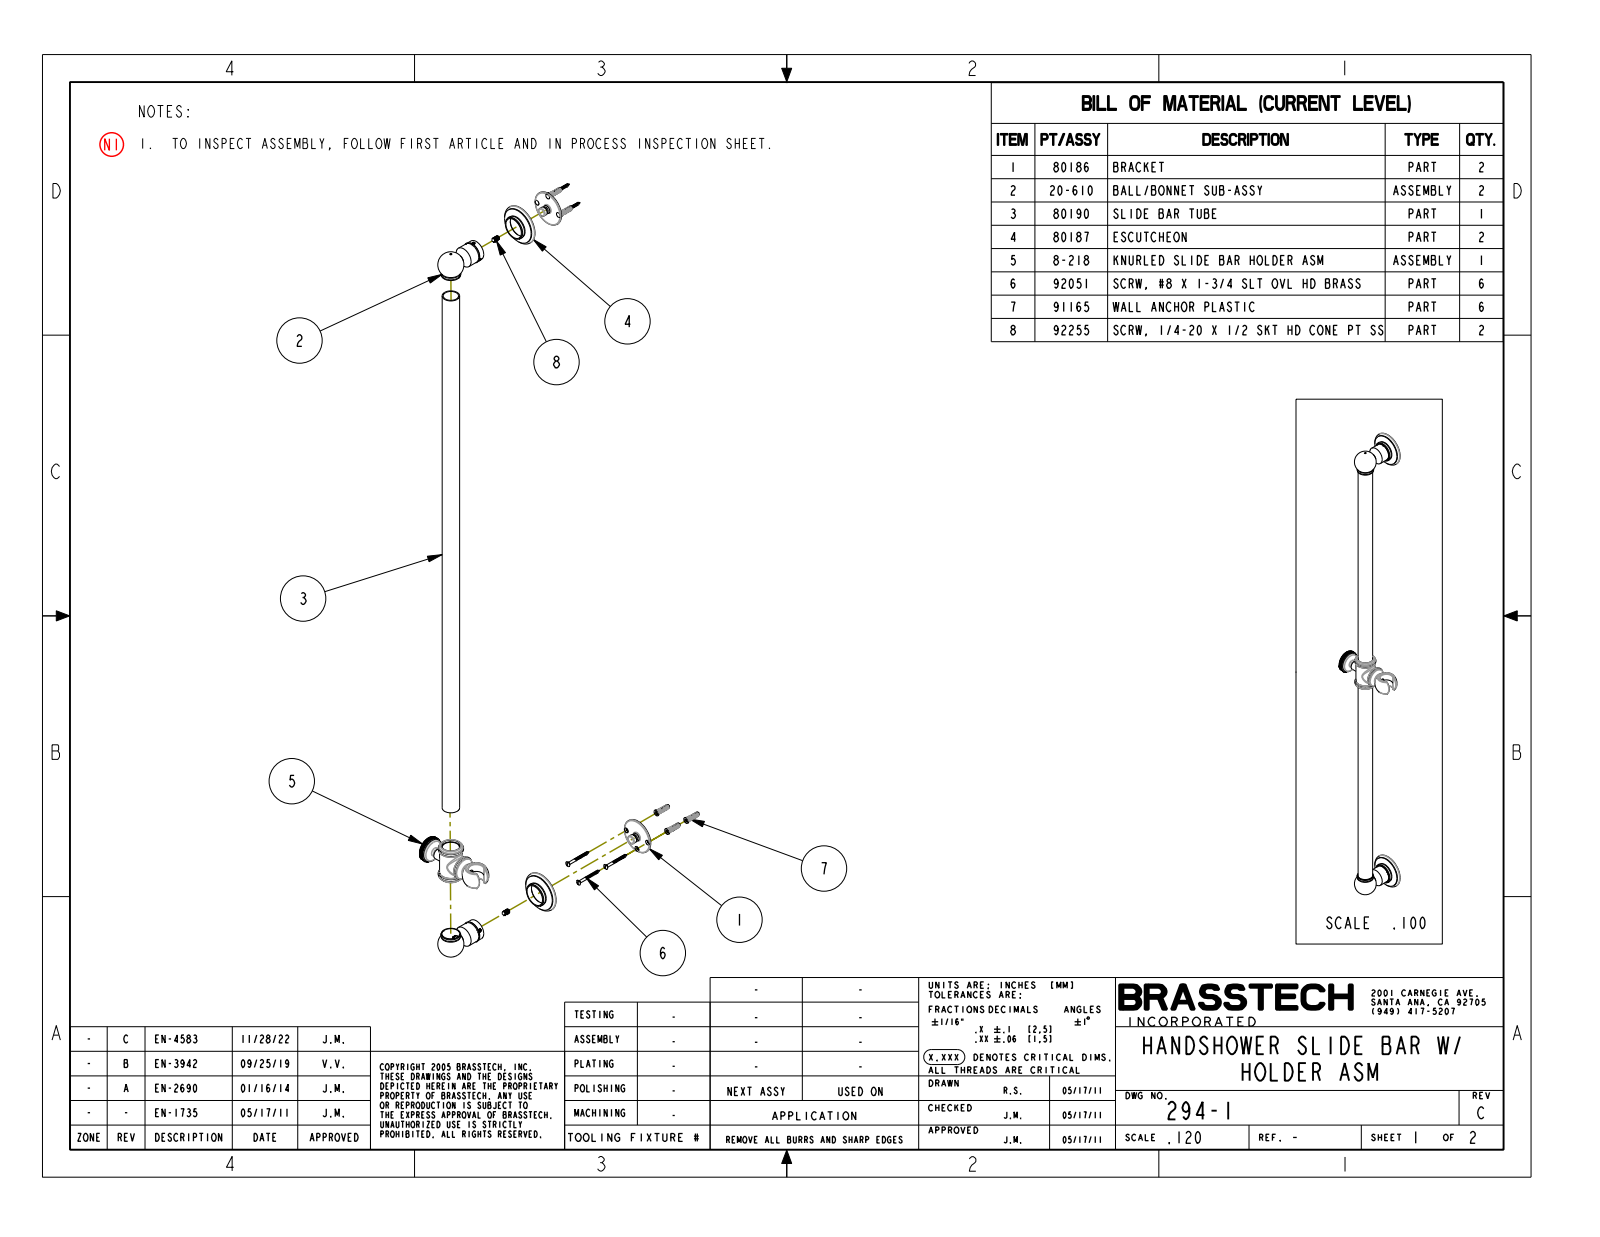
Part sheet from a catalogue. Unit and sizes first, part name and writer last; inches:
Units: inches
Overall size (bounding box): 37.88 × 4.584 × 2.892
Round bosses / shafts (diameter × count): ⌀2.38 ×2, ⌀2.154 ×2, ⌀1.35 ×2, ⌀1.3 ×2, ⌀1.219 ×2, ⌀1.38 ×1, ⌀1.378 ×1, ⌀1.17 ×1
Partial cylindrical surfaces — rounded edges, fillets, slot ends (radius × count): R0.025 ×2, R0.748 ×1
Main face-to-face distances: 0.537, 0.344, 1.844, 1.5, 2.724, 2.189, 15.989, 16.333, 17.833, 18.178
Bodies: 0 solids, 401 faces (147 planar, 167 cylindrical, 87 other)
Part name (STEP PRODUCT): 294-1_SW0001
STEP written by: PRO/ENGINEER BY PARAMETRIC TECHNOLOGY CORPORATION, 2009300 (CONFIG_CONTROL_DESIGN)
